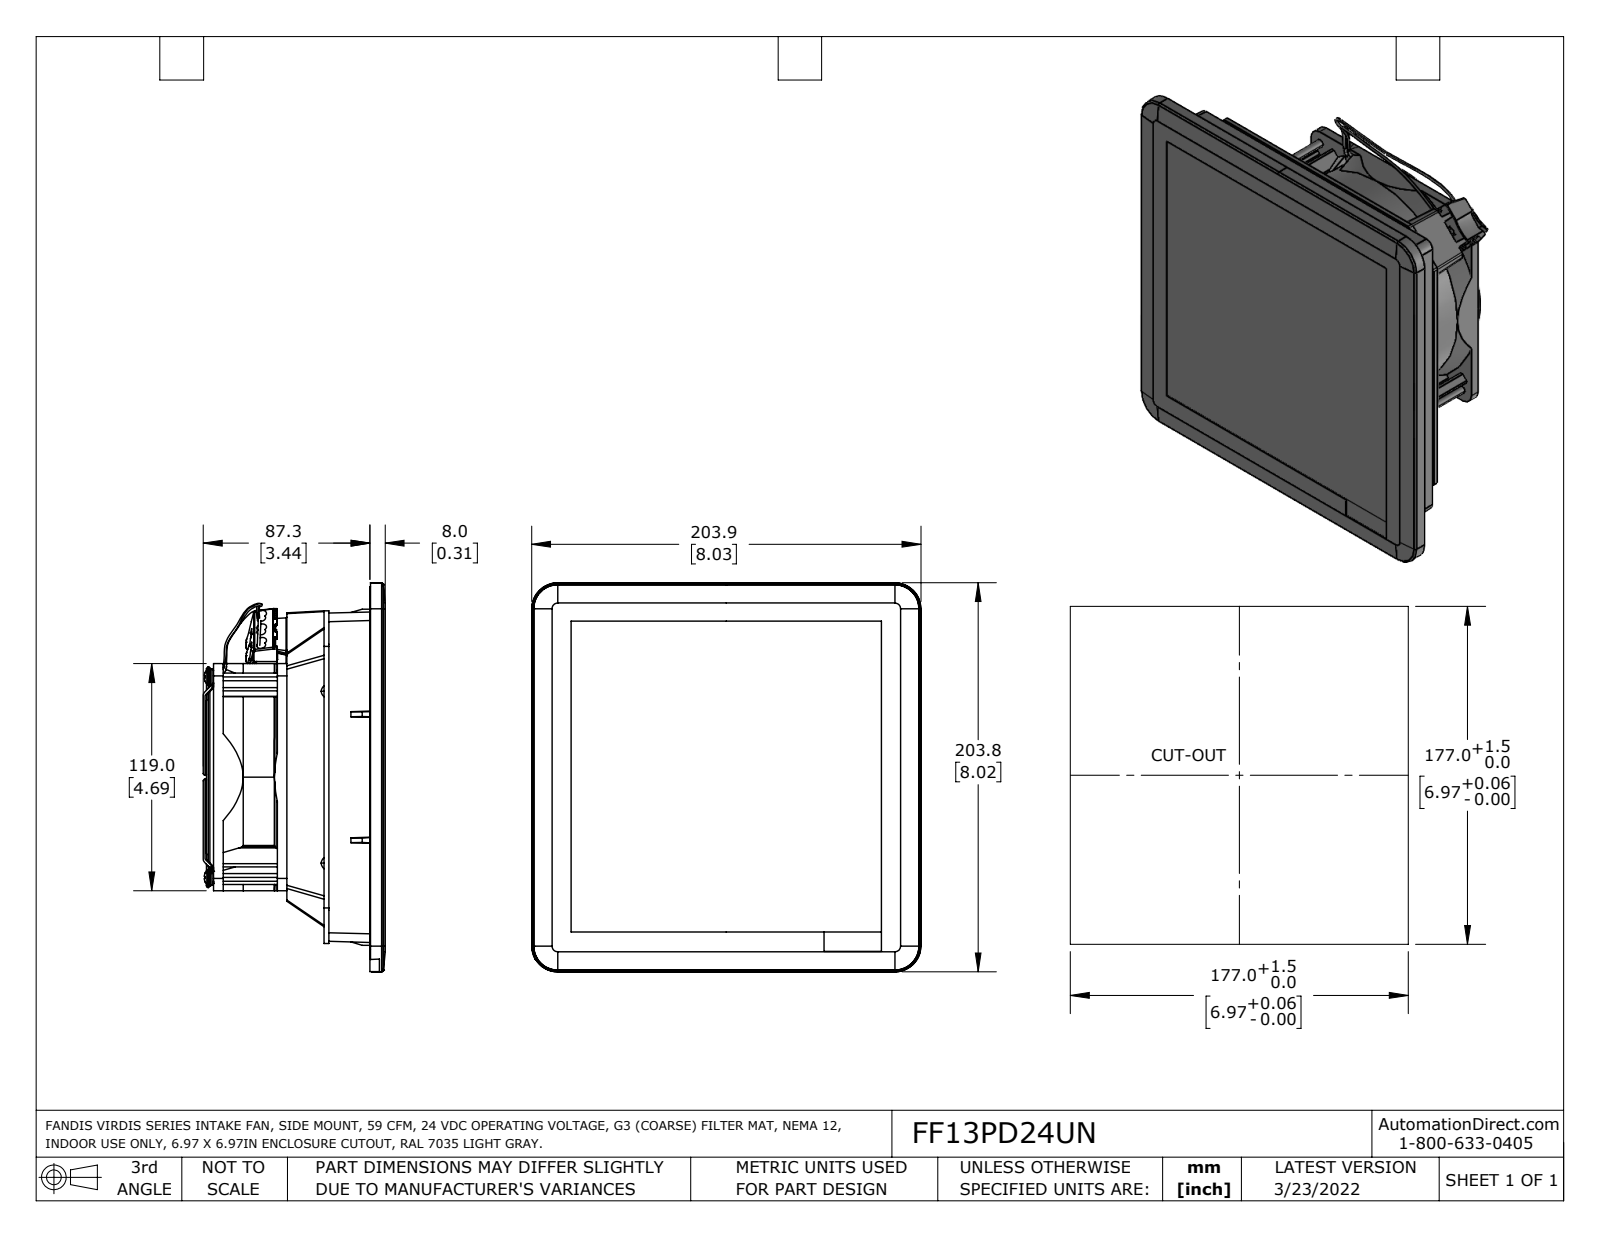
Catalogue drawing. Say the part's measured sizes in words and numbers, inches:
The part is named "FF13PDxxyN (p.c.)". Its 3-D file was written by "SolidWorks 2021 (AUTOMOTIVE_DESIGN)". It is 7 solids with 1102 faces: 524 planar, 306 cylindrical and 272 other. Overall it measures 8.028 by 8.027 by 3.752 inches. Its volume is 116.6 cubic inches and its surface area 256.3 square inches. Round holes: 4 of diameter 0.169. Round bosses or shafts: 4 of diameter 0.315, 4 of diameter 0.157, 1 of diameter 4.685. Partial cylindrical surfaces (rounded edges, fillets, slot ends): 33 of radius 0.012, 30 of radius 0.02, 30 of radius 0.039, 13 of radius 0.016, 13 of radius 0.028, 12 of radius 0.059, 10 of radius 0.177, 9 of radius 0.024. The main face-to-face distances are 3.52, 3.224, 0.295, 0.02, 0.315, 3.539, 1.26, 2.28, 1.24, 0.945. The hole center spacings are 4.134, 5.846.
